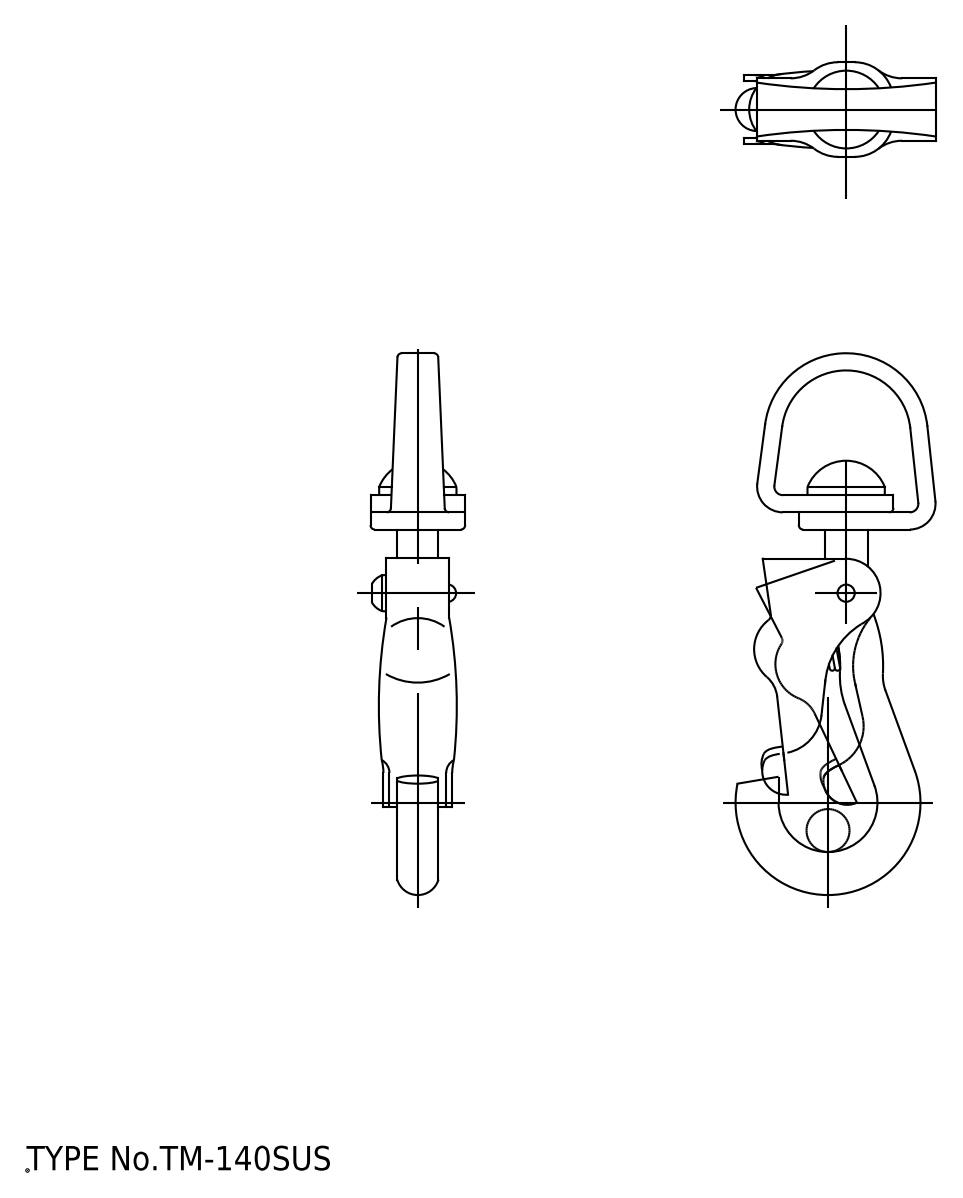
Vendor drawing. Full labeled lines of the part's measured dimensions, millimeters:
Part name (STEP PRODUCT): Dカン; フック; レバー
STEP written by: spGate 20.6.3 (****-****-****-****) (AUTOMOTIVE_DESIGN)
Units: millimetres
Bodies: 3 solids, 201 faces (48 planar, 85 cylindrical, 68 other)
Overall size (bounding box): 63 × 23.23 × 11
Volume: 2 812 mm³ · Surface area: 3 696 mm²
Round holes (diameter × count): ⌀2 ×1, ⌀7 ×1
Partial cylindrical surfaces — rounded edges, fillets, slot ends (radius × count): R2 ×14, R4.5 ×8, R0.7 ×7, R3 ×4, R0.5 ×2, R1 ×2, R1.2 ×2, R1.7 ×2
Main face-to-face distances: 0.7, 0.55, 5.35, 6.6, 6.05, 1.25, 2, 4, 5.9, 4.8
